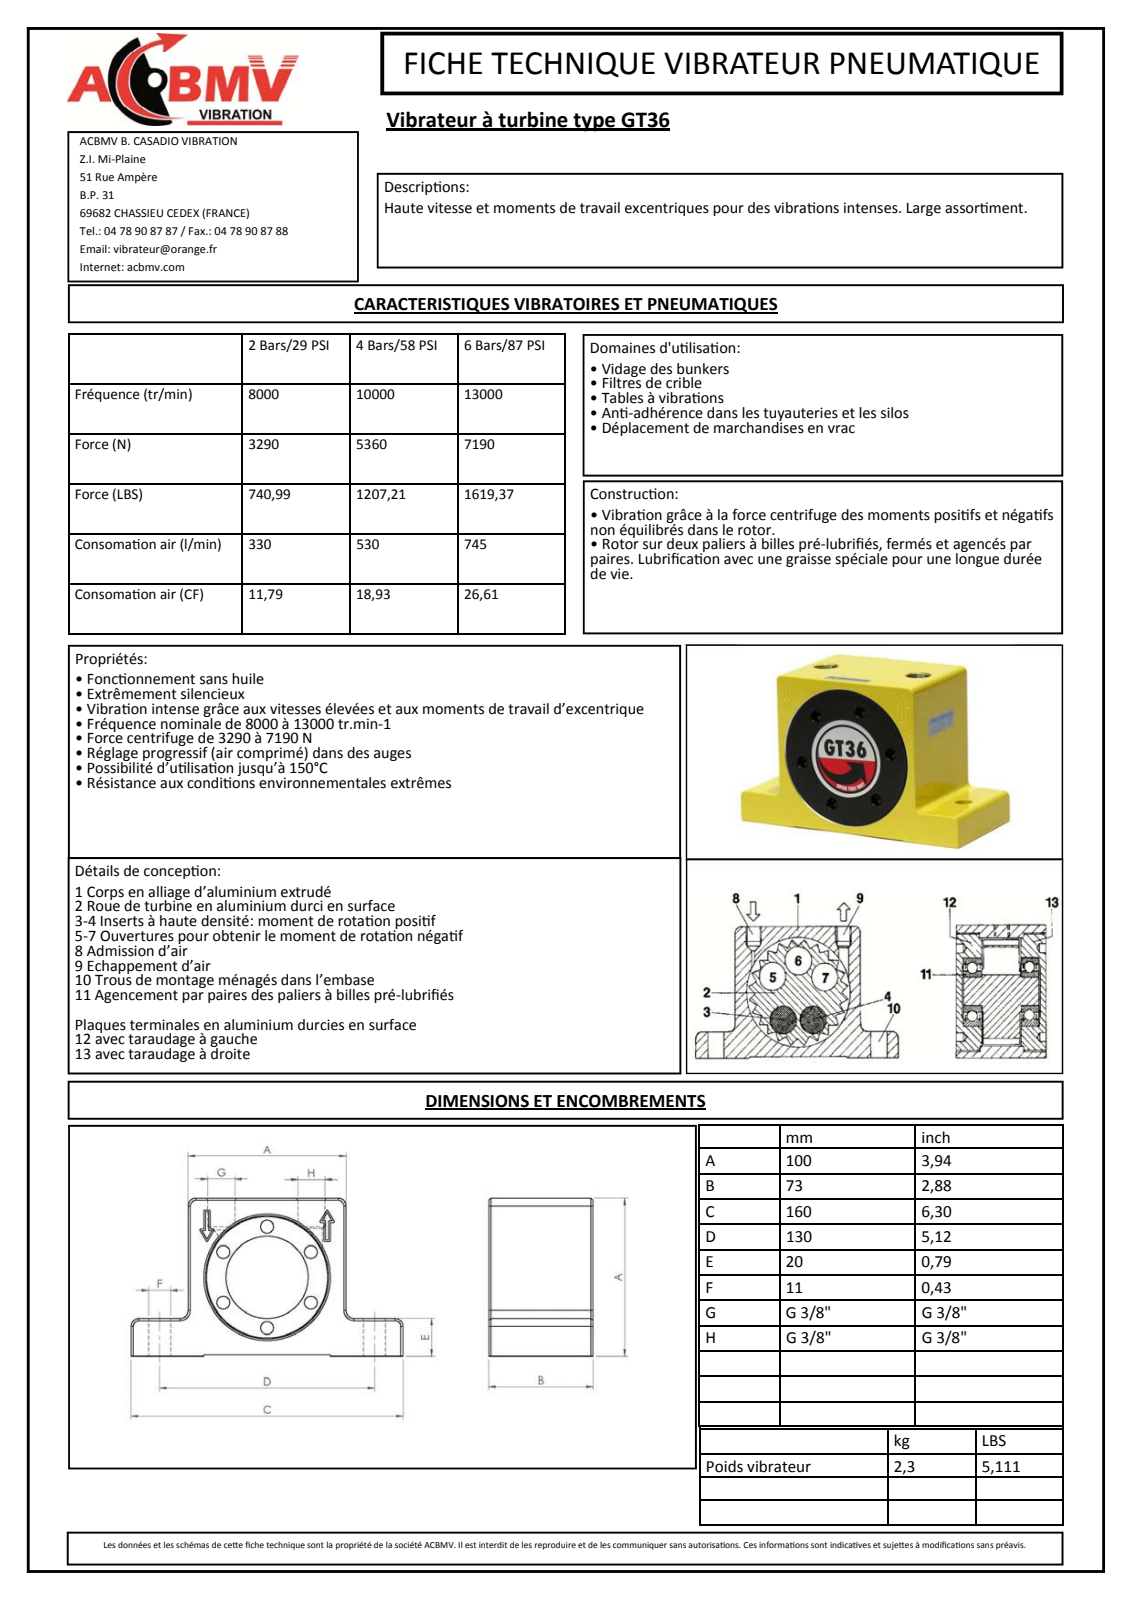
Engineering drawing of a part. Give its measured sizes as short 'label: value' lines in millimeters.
name: 8036-00-M
written by: Autodesk Inventor 2011 (CONFIG_CONTROL_DESIGN)
unit: mm
bodies: 1 solid, 275 faces (172 planar, 73 cylindrical, 30 other)
size: 160 × 100 × 73
volume: 781 808 mm³; area: 68 469 mm²
holes: 6× ⌀7, 4× ⌀11, 2× ⌀14.95, 1× ⌀2.98, 1× ⌀51
bosses: 1× ⌀2.68
rounds: 14× R0.3, 6× R4, 4× R0.77, 3× R0.9, 3× R1.03, 3× R2.06, 2× R0.39, 2× R0.52
face distances: 100, 0.5, 72.7, 99.5, 73, 0.8, 72.2, 71.9, 72.4, 80
hole spacings: 33, 57.16, 66, 24.34, 31, 40.31, 55.17, 55.68
